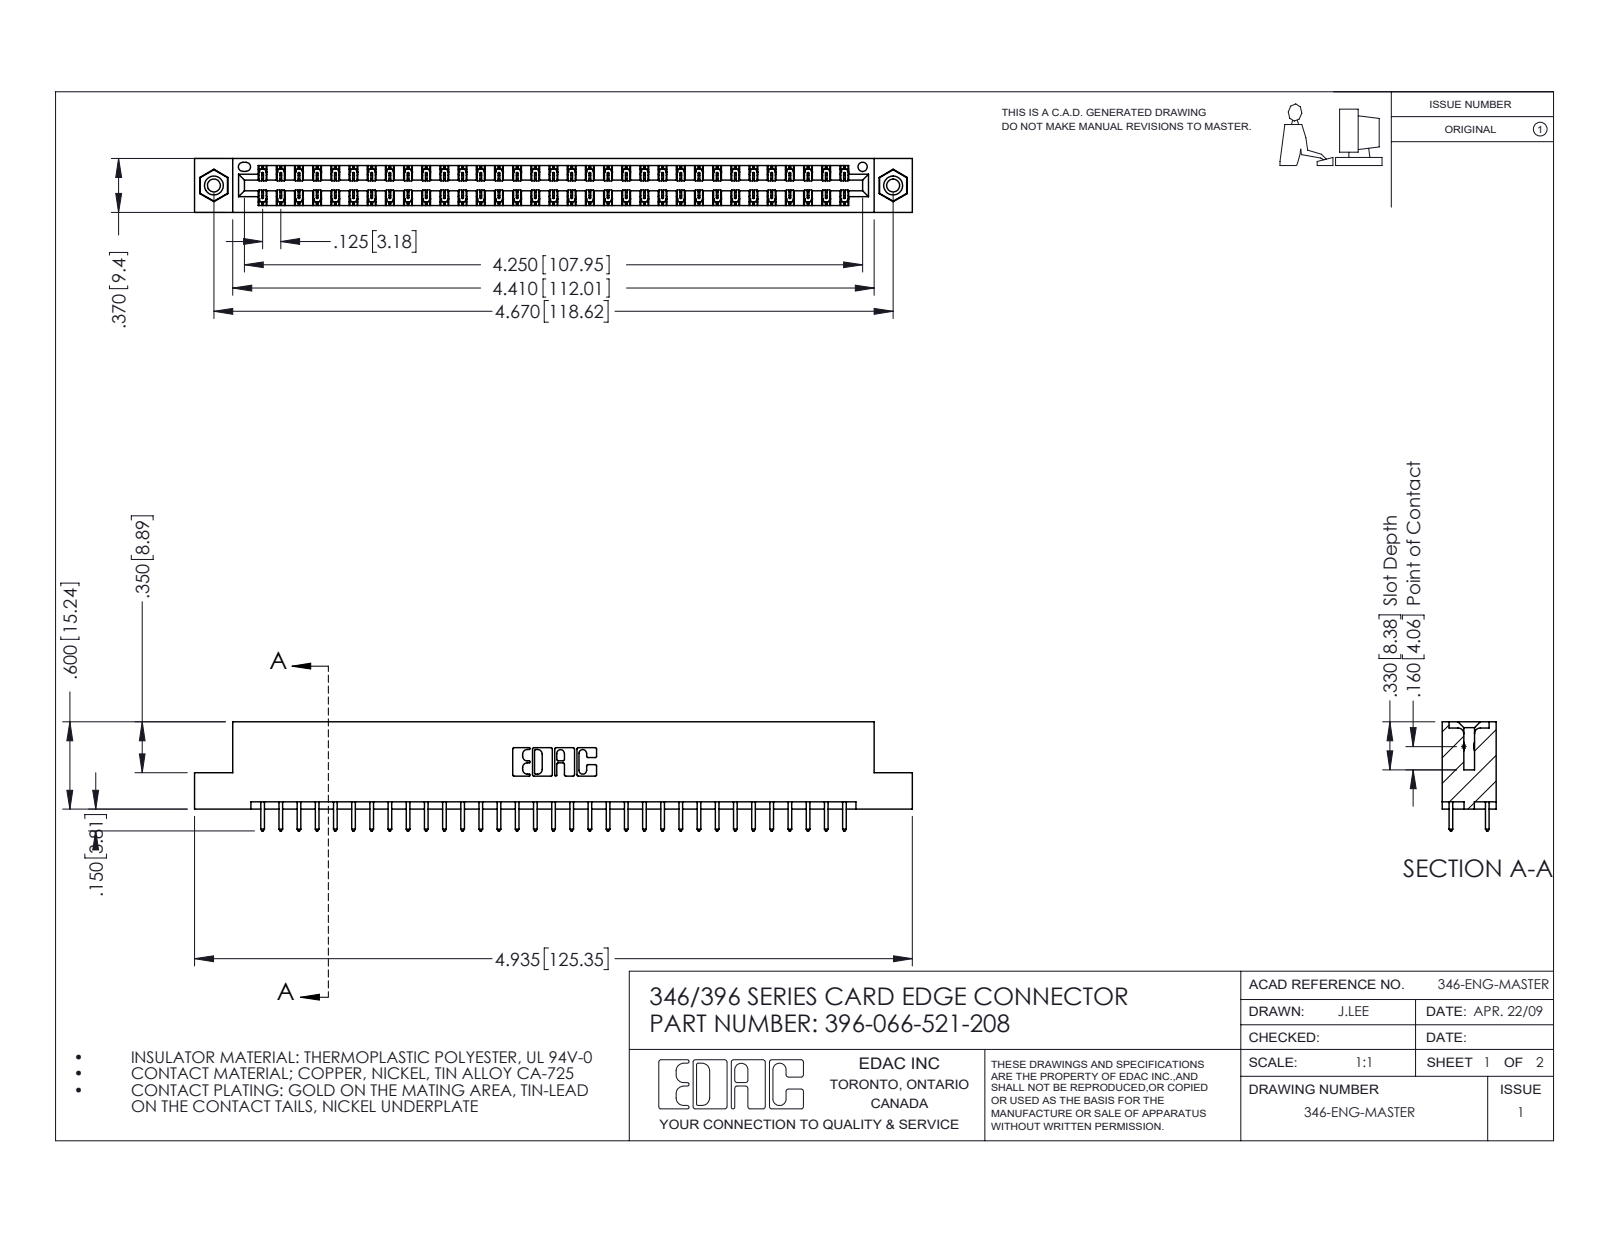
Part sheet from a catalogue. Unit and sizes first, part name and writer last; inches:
Units: inches
Overall size (bounding box): 4.935 × 0.75 × 0.37
Round holes (diameter × count): ⌀0.089 ×2, ⌀0.125 ×2, ⌀0.156 ×2, ⌀0.064 ×1
Round bosses / shafts (diameter × count): ⌀0.155 ×2
Partial cylindrical surfaces — rounded edges, fillets, slot ends (radius × count): R0.006 ×99, R0.01 ×66, R0.01 ×22, R0.007 ×6, R0.031 ×6, R0.026 ×3, R0.014 ×2, R0.022 ×2
Main face-to-face distances: 0.048, 0.322, 0.25, 0.37, 0.072, 0.298, 0.025, 0.275, 0.148, 0.222
Hole centre spacings: 0.246, 4.462, 4.67
Volume: 0.74 in³ · Surface area: 25.35 in²
Bodies: 69 solids, 3614 faces (2418 planar, 1180 cylindrical, 16 other)
Part name (STEP PRODUCT): 346 Part_Flush Mounting Lugs - 0.156 Dia-TI; 396-066-521-208; 345-250-001_345-250-003-102; 345-292-001_345-293-121
STEP written by: SolidWorks 2016 (CONFIG_CONTROL_DESIGN)
